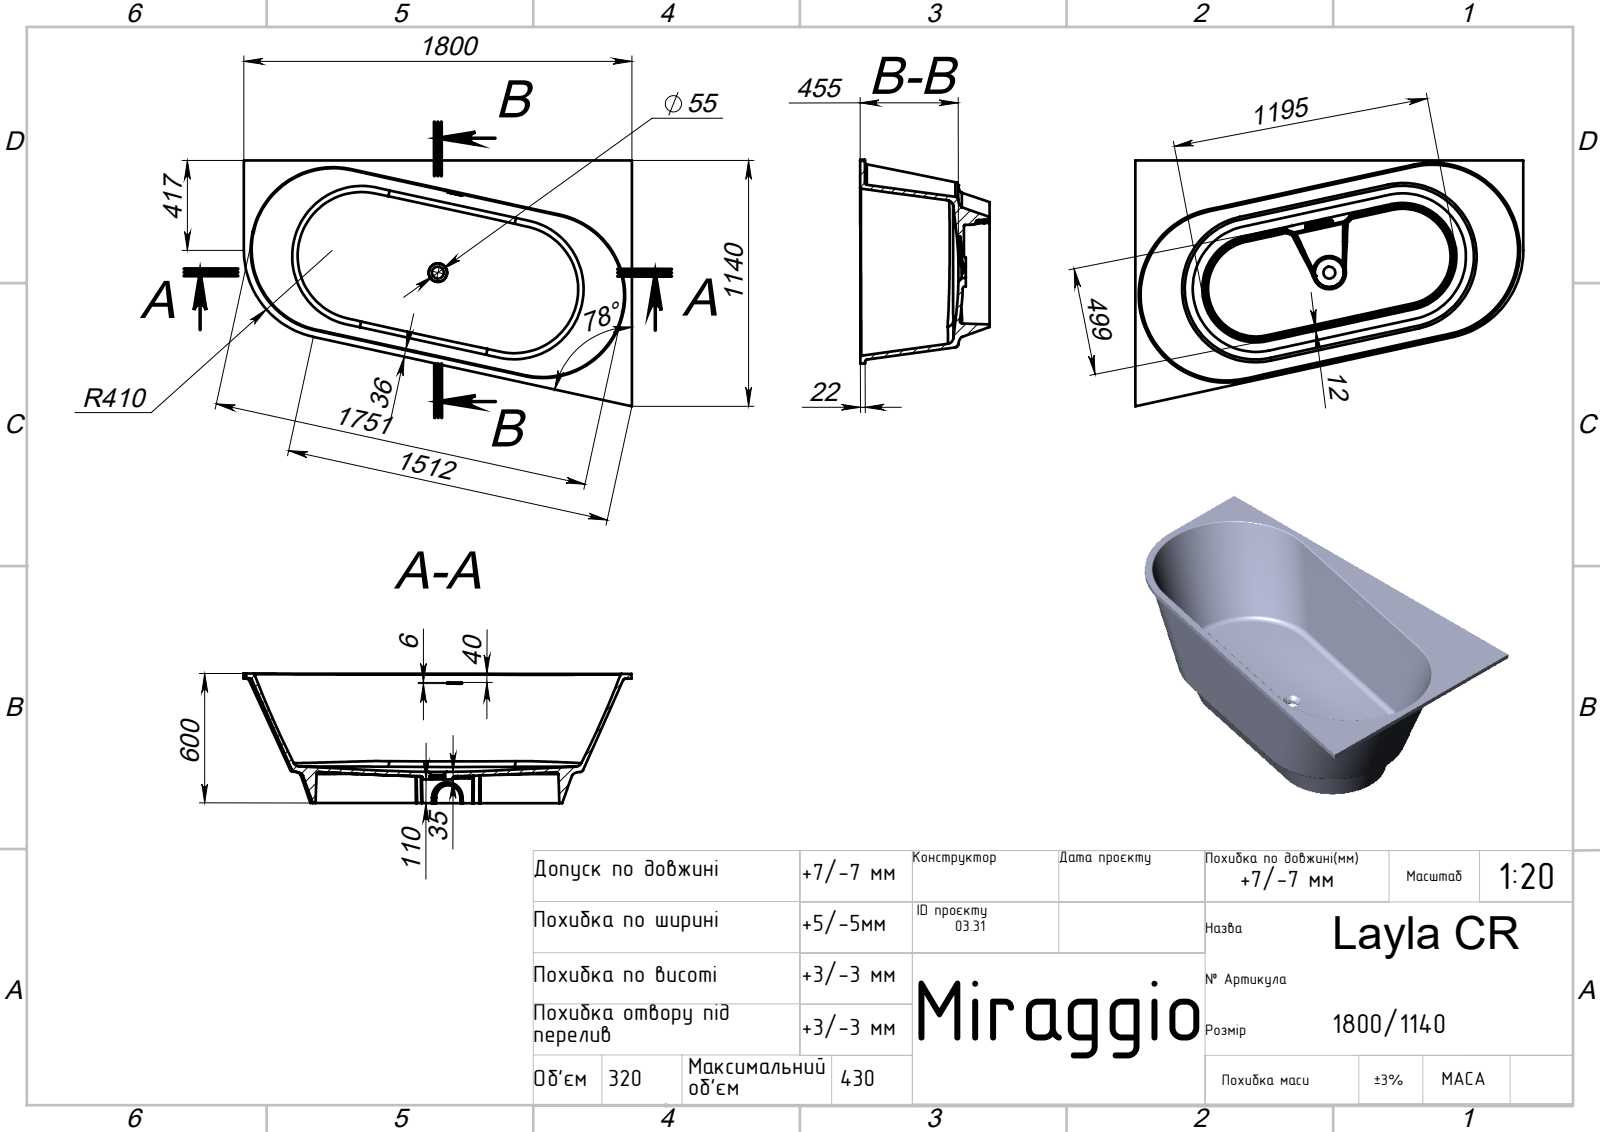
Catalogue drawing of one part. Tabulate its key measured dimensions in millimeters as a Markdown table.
| quantity | value |
| --- | --- |
| part name | Layla CR |
| STEP written by | SolidWorks 2020 (AUTOMOTIVE_DESIGN) |
| units | millimeters |
| bodies | 1 solid, 125 faces (28 planar, 19 cylindrical, 78 other) |
| overall size | 2001.85 × 1113.86 × 600 |
| volume | 75 790 000 mm³ |
| surface area | 6 912 000 mm² |
| round holes (diameter × count) | 55 × 1 |
| partial cylindrical surfaces (radius × count) | 10 × 4, 5 × 3, 3 × 2, 37 × 1, 46 × 1, 62.5 × 1, 198.58 × 1, 237.27 × 1 |
| main face-to-face distances | 22, 578, 600, 119, 459, 481, 110, 9, 468, 490 |
